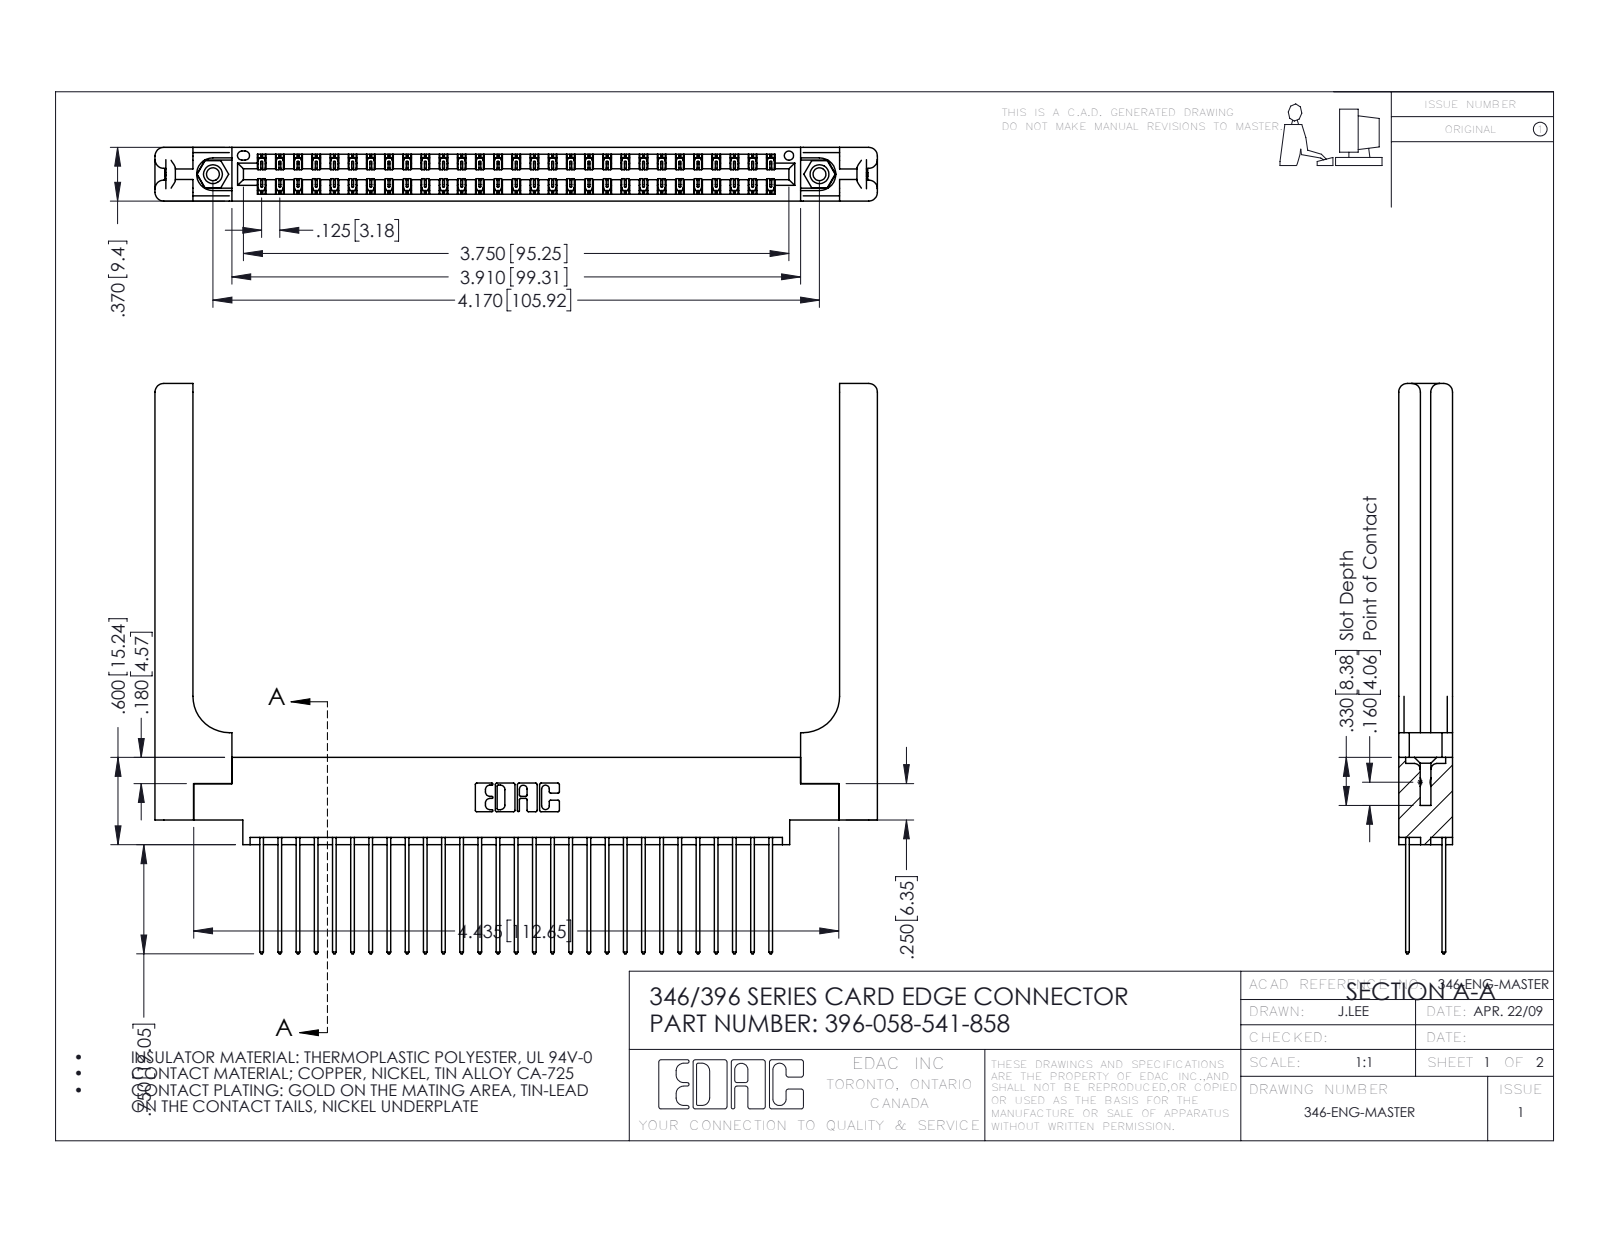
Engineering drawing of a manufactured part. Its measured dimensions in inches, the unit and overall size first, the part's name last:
Units: inches
Overall size (bounding box): 4.966 × 3.92 × 0.37
Round holes (diameter × count): ⌀0.089 ×2, ⌀0.125 ×2, ⌀0.156 ×2, ⌀0.064 ×1
Round bosses / shafts (diameter × count): ⌀0.155 ×2
Partial cylindrical surfaces — rounded edges, fillets, slot ends (radius × count): R0.006 ×87, R0.01 ×58, R0.01 ×22, R0.06 ×16, R0.007 ×6, R0.031 ×6, R0.026 ×3, R0.014 ×2
Main face-to-face distances: 0.048, 0.322, 0.37, 0.072, 0.25, 0.025, 0.298, 0.15, 0.148, 0.275
Hole centre spacings: 0.246, 3.962, 4.17
Volume: 1.213 in³ · Surface area: 36.51 in²
Bodies: 63 solids, 3398 faces (2258 planar, 1080 cylindrical, 60 other)
Part name (STEP PRODUCT): 346 Part_0.170 Offset - 0.156 Dia-TH; 396-058-541-858; 346-220-058_345-220-058; 345-250-001_345-250-001-102 (+1 more)
STEP written by: SolidWorks 2016 (CONFIG_CONTROL_DESIGN)
